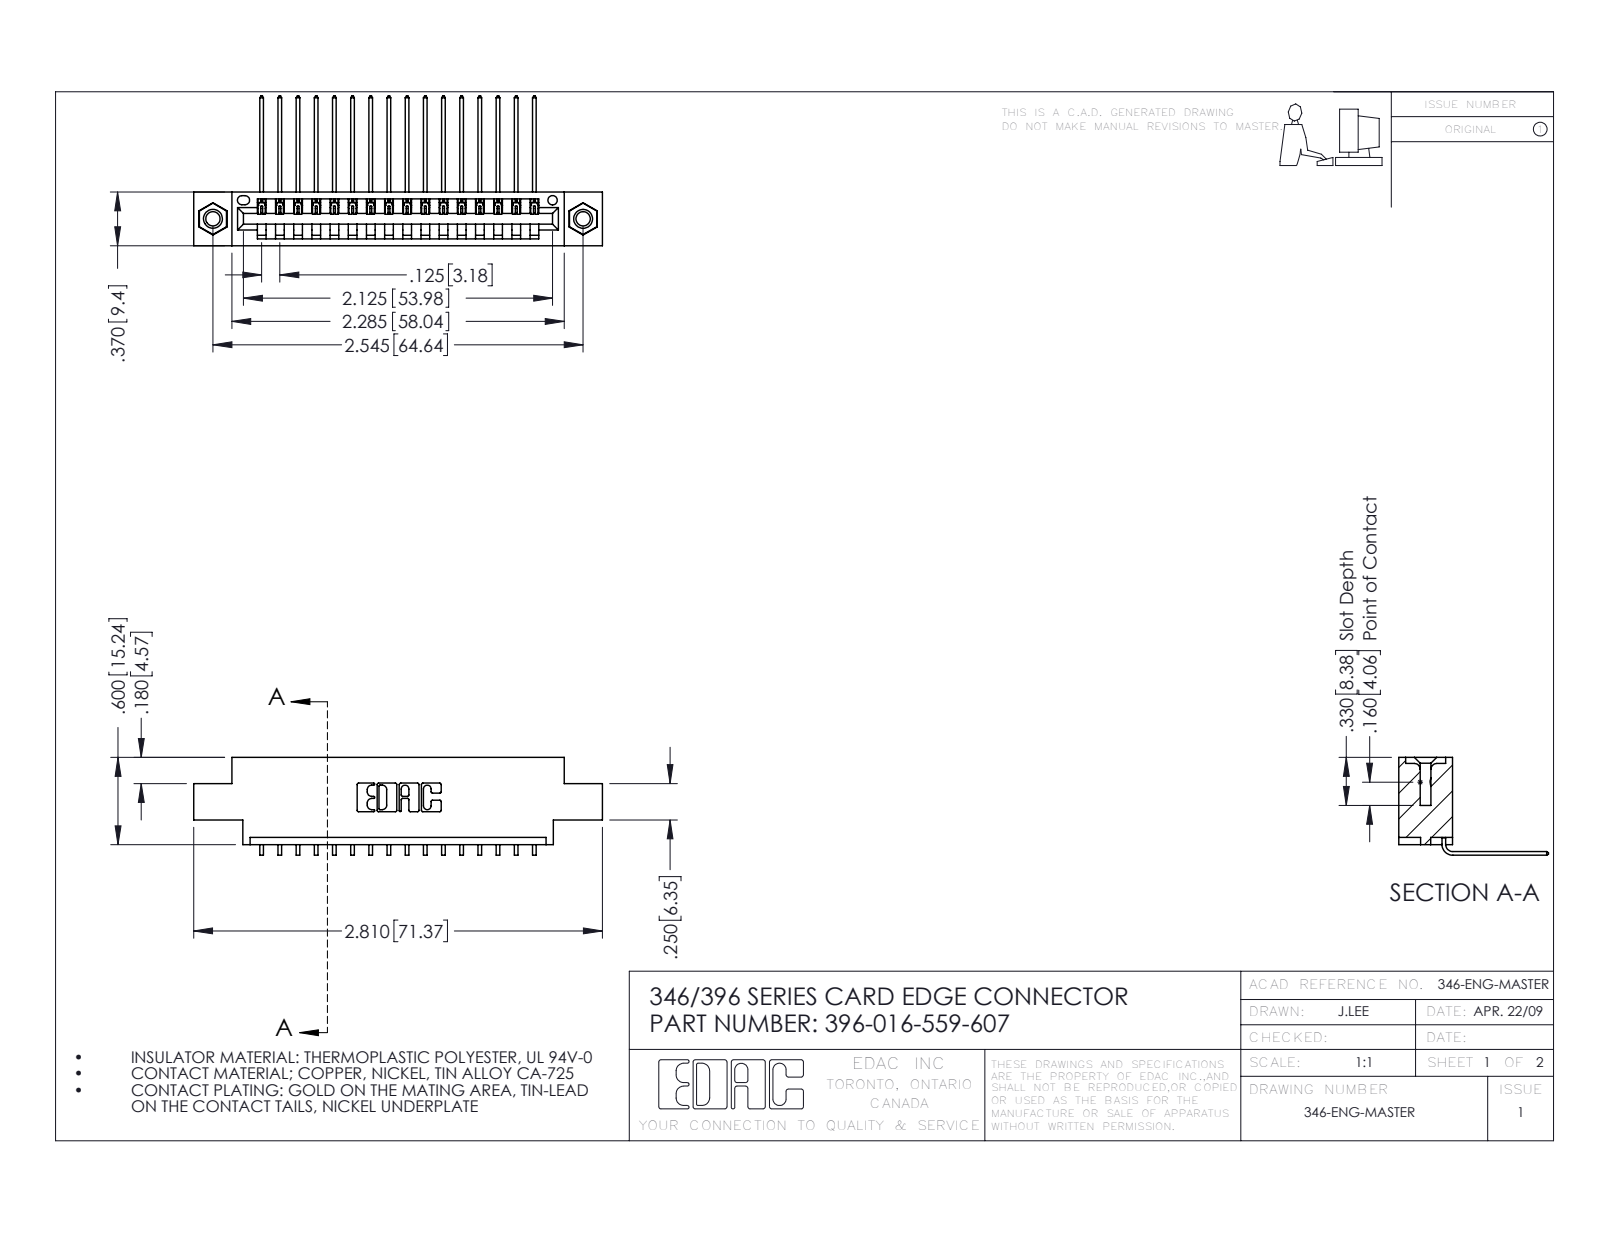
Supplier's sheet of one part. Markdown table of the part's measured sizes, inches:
| quantity | value |
| --- | --- |
| part name | 396-016-559-607; 345-292-001_558 559 Tail - 1; 345-250-001_345-250-005-103; 346 Part_0.170 Offset - 0.156 Dia-TI |
| STEP written by | SolidWorks 2016 (CONFIG_CONTROL_DESIGN) |
| units | inches |
| bodies | 19 solids, 1146 faces (784 planar, 346 cylindrical, 16 other) |
| overall size | 2.81 × 1.03 × 0.673 |
| volume | 0.399 in³ |
| surface area | 13.03 in² |
| round holes (diameter × count) | 0.098 × 2, 0.125 × 2, 0.156 × 2, 0.064 × 1 |
| round bosses / shafts (diameter × count) | 0.155 × 2 |
| partial cylindrical surfaces (radius × count) | 0.006 × 32, 0.01 × 22, 0.007 × 6, 0.031 × 6, 0.026 × 3, 0.031 × 2, 0.04 × 2, 0.014 × 1 |
| main face-to-face distances | 0.048, 0.37, 0.322, 0.25, 0.025, 0.072, 0.222, 0.148, 0.1, 0.174 |
| hole center spacings | 0.246, 2.338, 2.545 |
